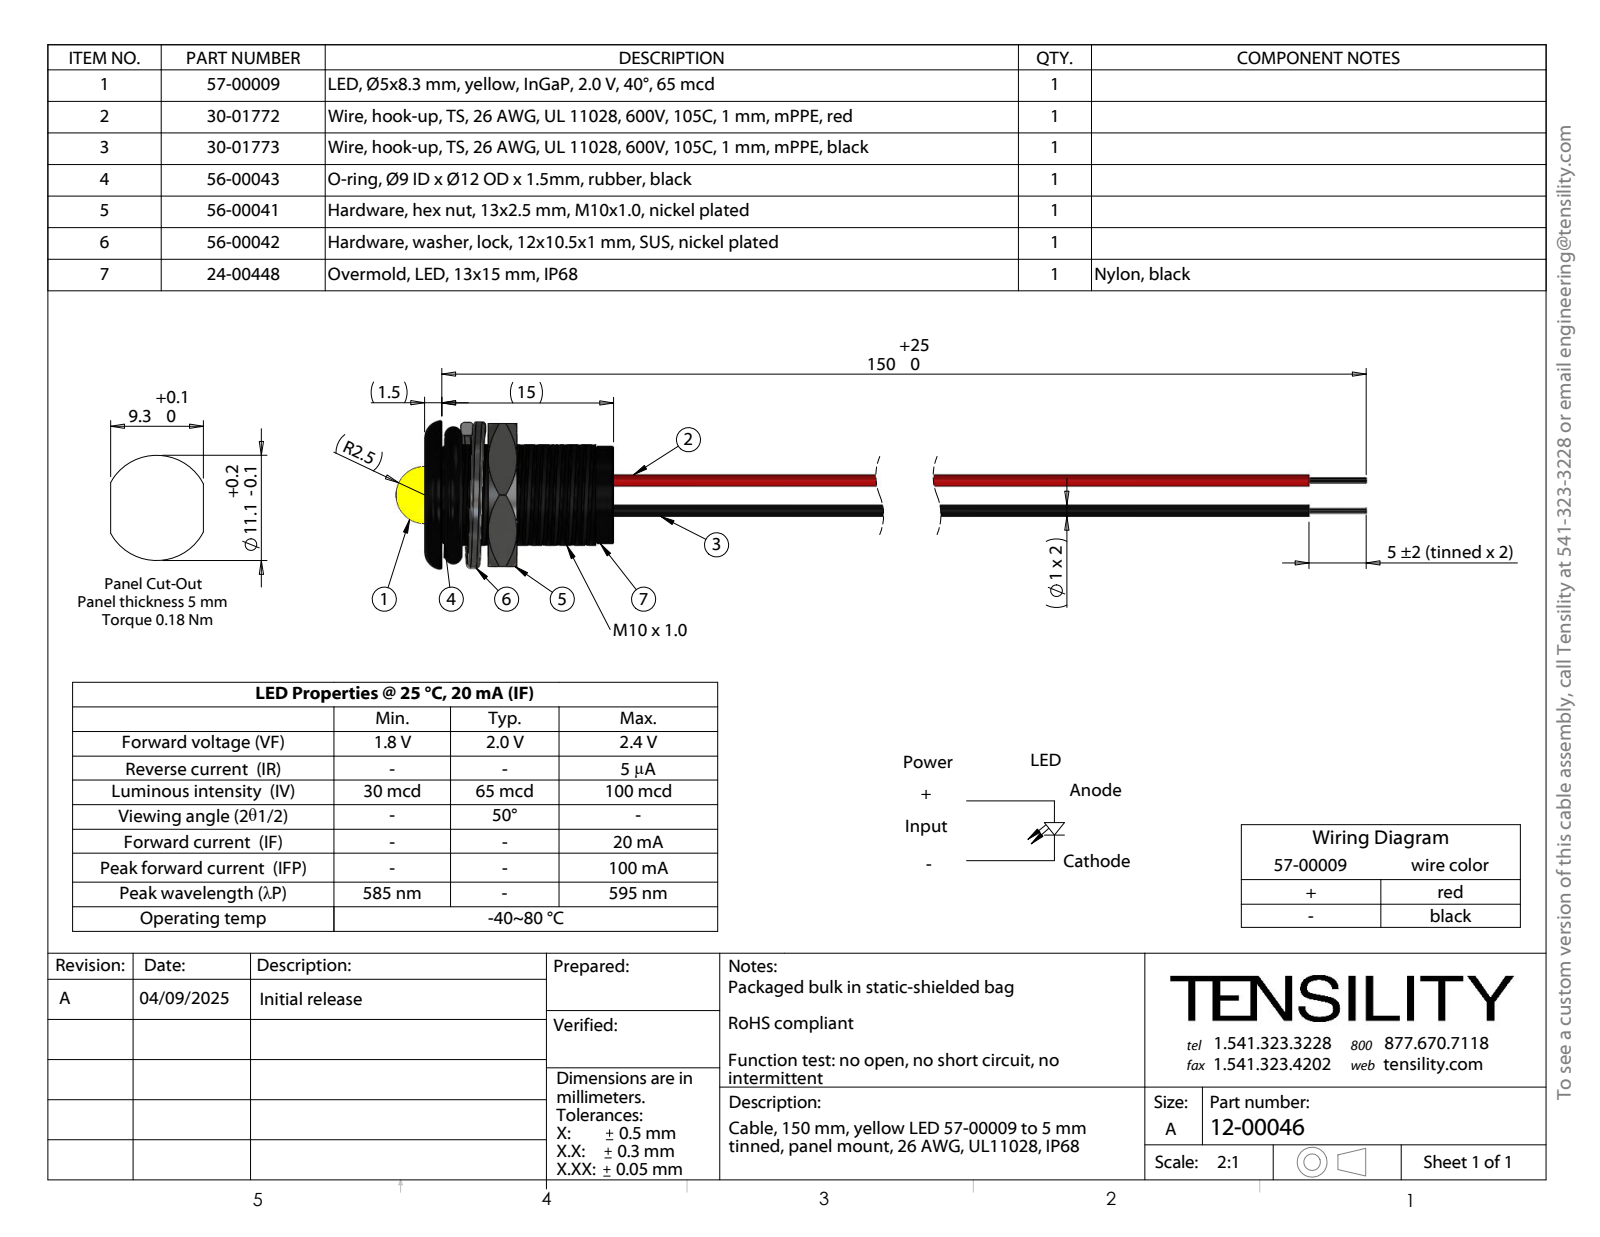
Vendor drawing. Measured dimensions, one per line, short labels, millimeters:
name: 30-01773_stripped and tinned; 56-00041; 57-00009_trimmed leads; 24-00448 (+4 more)
written by: SolidWorks 2021 (CONFIG_CONTROL_DESIGN)
unit: mm
bodies: 57 solids, 514 faces (185 planar, 246 cylindrical, 83 other)
size: 173.99 × 14.43 × 12.99
volume: 1 769 mm³; area: 6 568 mm²
holes: 2× ⌀1
bosses: 2× ⌀1, 2× ⌀0.83, 1× ⌀8.5, 1× ⌀5
rounds: 1× R4.33, 1× R5
face distances: 1.5, 16.5, 15, 12.5, 8.06, 6.56, 8.44, 5.56, 4.06, 2.5
hole spacings: 0.36, 0.38, 0.33, 2.43, 2.35, 2.48, 2.52, 2.56
